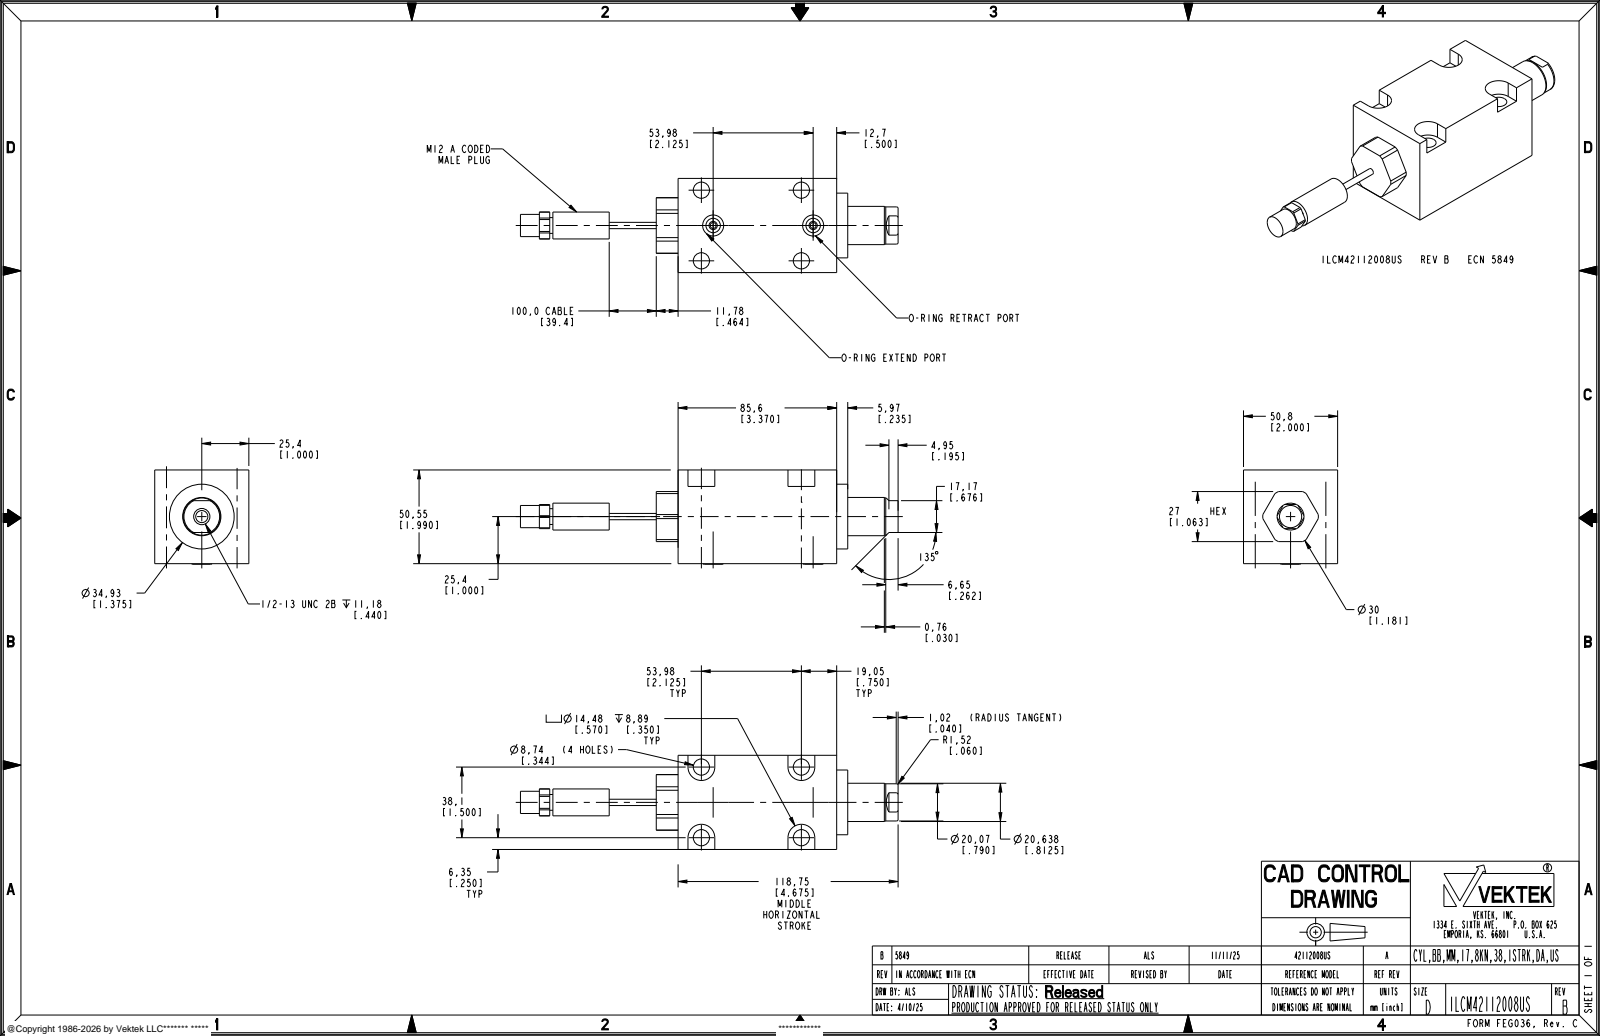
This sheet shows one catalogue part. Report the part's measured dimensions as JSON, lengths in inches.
{"part_name": "ILCM42112008US", "step_written_by": "CREO PARAMETRIC BY PTC INC, 2021164 (AUTOMOTIVE_DESIGN)", "units": "inches", "bodies": {"solids": 1, "faces": 120, "planar": 46, "cylindrical": 52, "other": 22}, "overall_size": [8.025, 2.2, 2.003], "volume_in3": 14.16, "surface_area_in2": 53.95, "round_holes": [[0.344, 4], [0.125, 2], [0.447, 2], [0.257, 1]], "round_bosses_or_shafts": [[1.375, 1], [0.813, 1], [0.79, 1], [0.571, 1], [0.472, 1], [0.335, 1], [0.312, 1], [0.134, 1]], "partial_cylinders_radius": [[0.285, 4], [0.591, 1]], "face_to_face_distances": [2, 1.99, 3.37, 0.235, 3.605, 4.069, 3.834, 0.464, 1.063, 1.64], "hole_center_spacings": [0.791, 2.125, 1.5, 2.019, 2.491, 2.601]}
